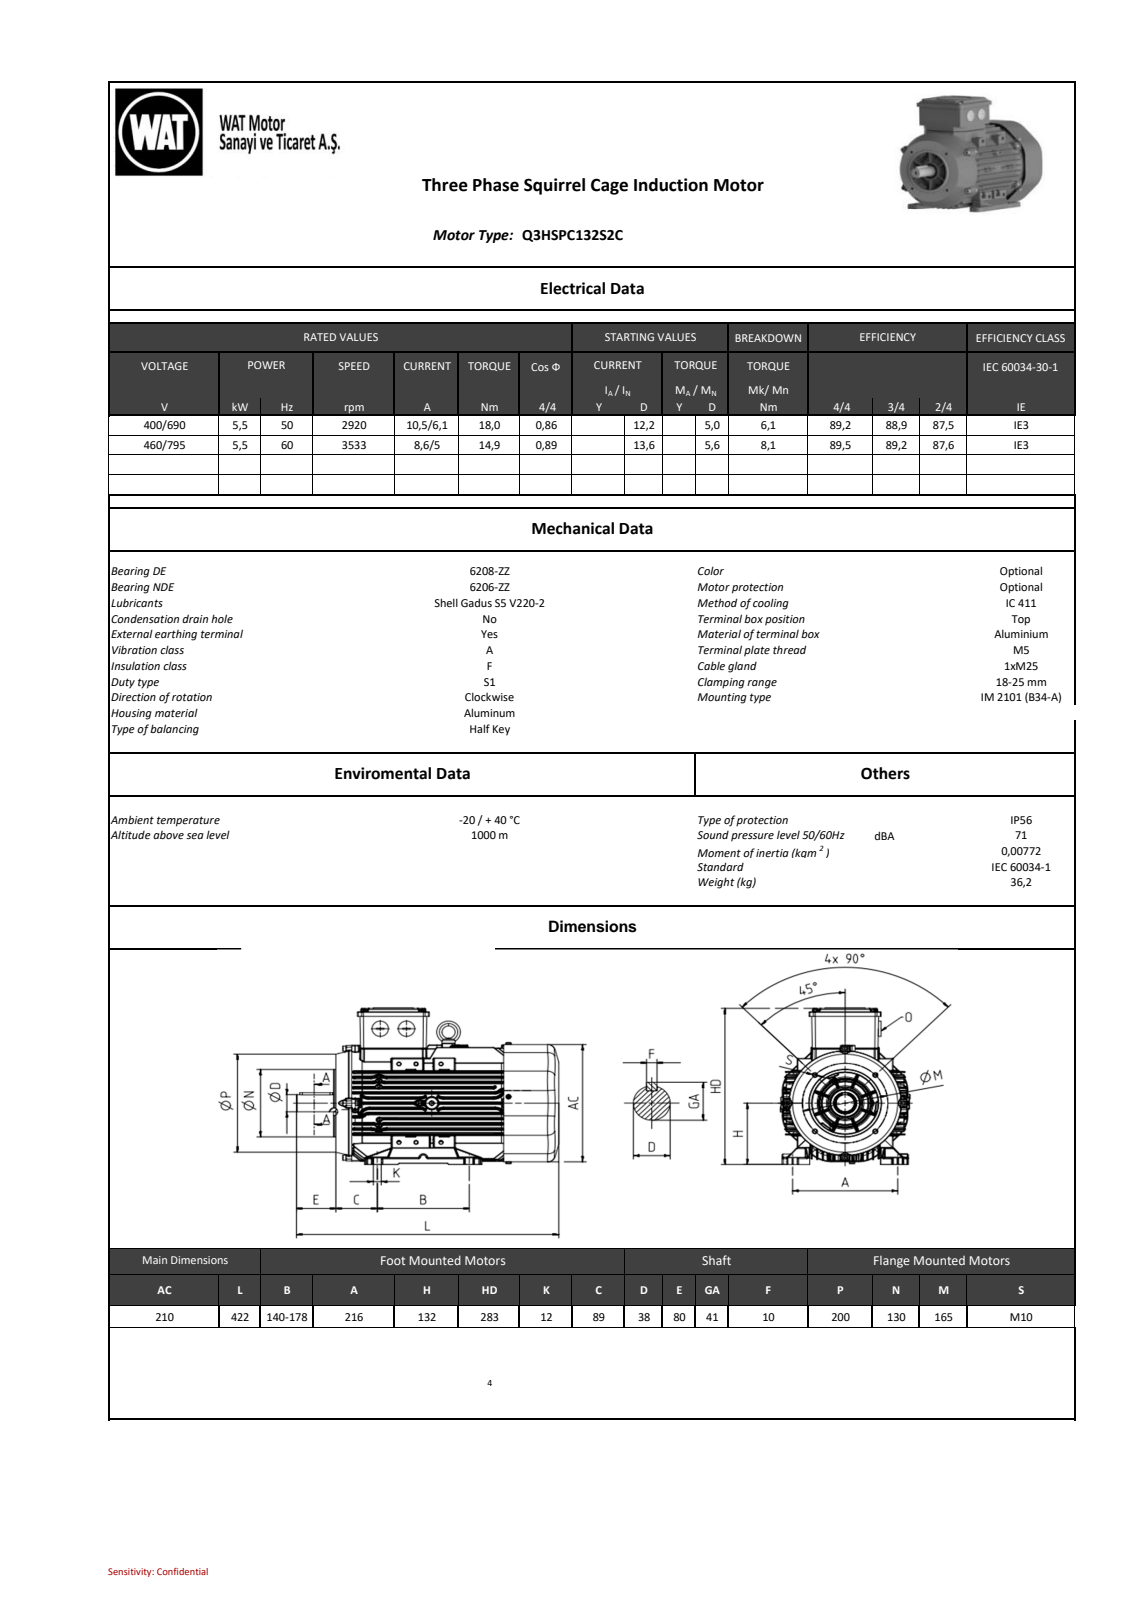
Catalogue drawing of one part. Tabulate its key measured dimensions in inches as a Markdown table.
| quantity | value |
| --- | --- |
| part name | QHS series_ 132_B34a_stp_objects |
| STEP written by | SIEMENS PLM Software NX2206.8101 (AP203_CONFIGURATION_CONTROLLED_3D_DESIGN_OF_MECHANICAL_PARTS_AND_ASSEMBLIES_MIM_LF) |
| units | inches |
| bodies | 0 solids, 6766 faces (1614 planar, 2658 cylindrical, 2494 other) |
| overall size | 16.614 × 11.141 × 9.633 |
| round holes (diameter × count) | 0.335 × 4, 0.197 × 2, 0.92 × 2, 0.315 × 1, 0.512 × 1, 2.26 × 1, 2.31 × 1 |
| round bosses / shafts (diameter × count) | 0.315 × 8, 0.465 × 4, 0.394 × 4, 0.236 × 4, 7.402 × 1, 5.118 × 1, 2.402 × 1, 1.575 × 1 |
| partial cylindrical surfaces (radius × count) | 0.079 × 552, 0.039 × 529, 0.031 × 488, 0.02 × 225, 0.118 × 64, 0.394 × 13, 0.197 × 9, 0.098 × 8 |
| main face-to-face distances | 0.197, 0.039, 0.846, 1.416, 0.433, 3.919, 0.983, 4.444, 0.321, 2.714 |
| hole center spacings | 3.248, 4.594, 1.949, 6.496, 1.575, 2.756 |
